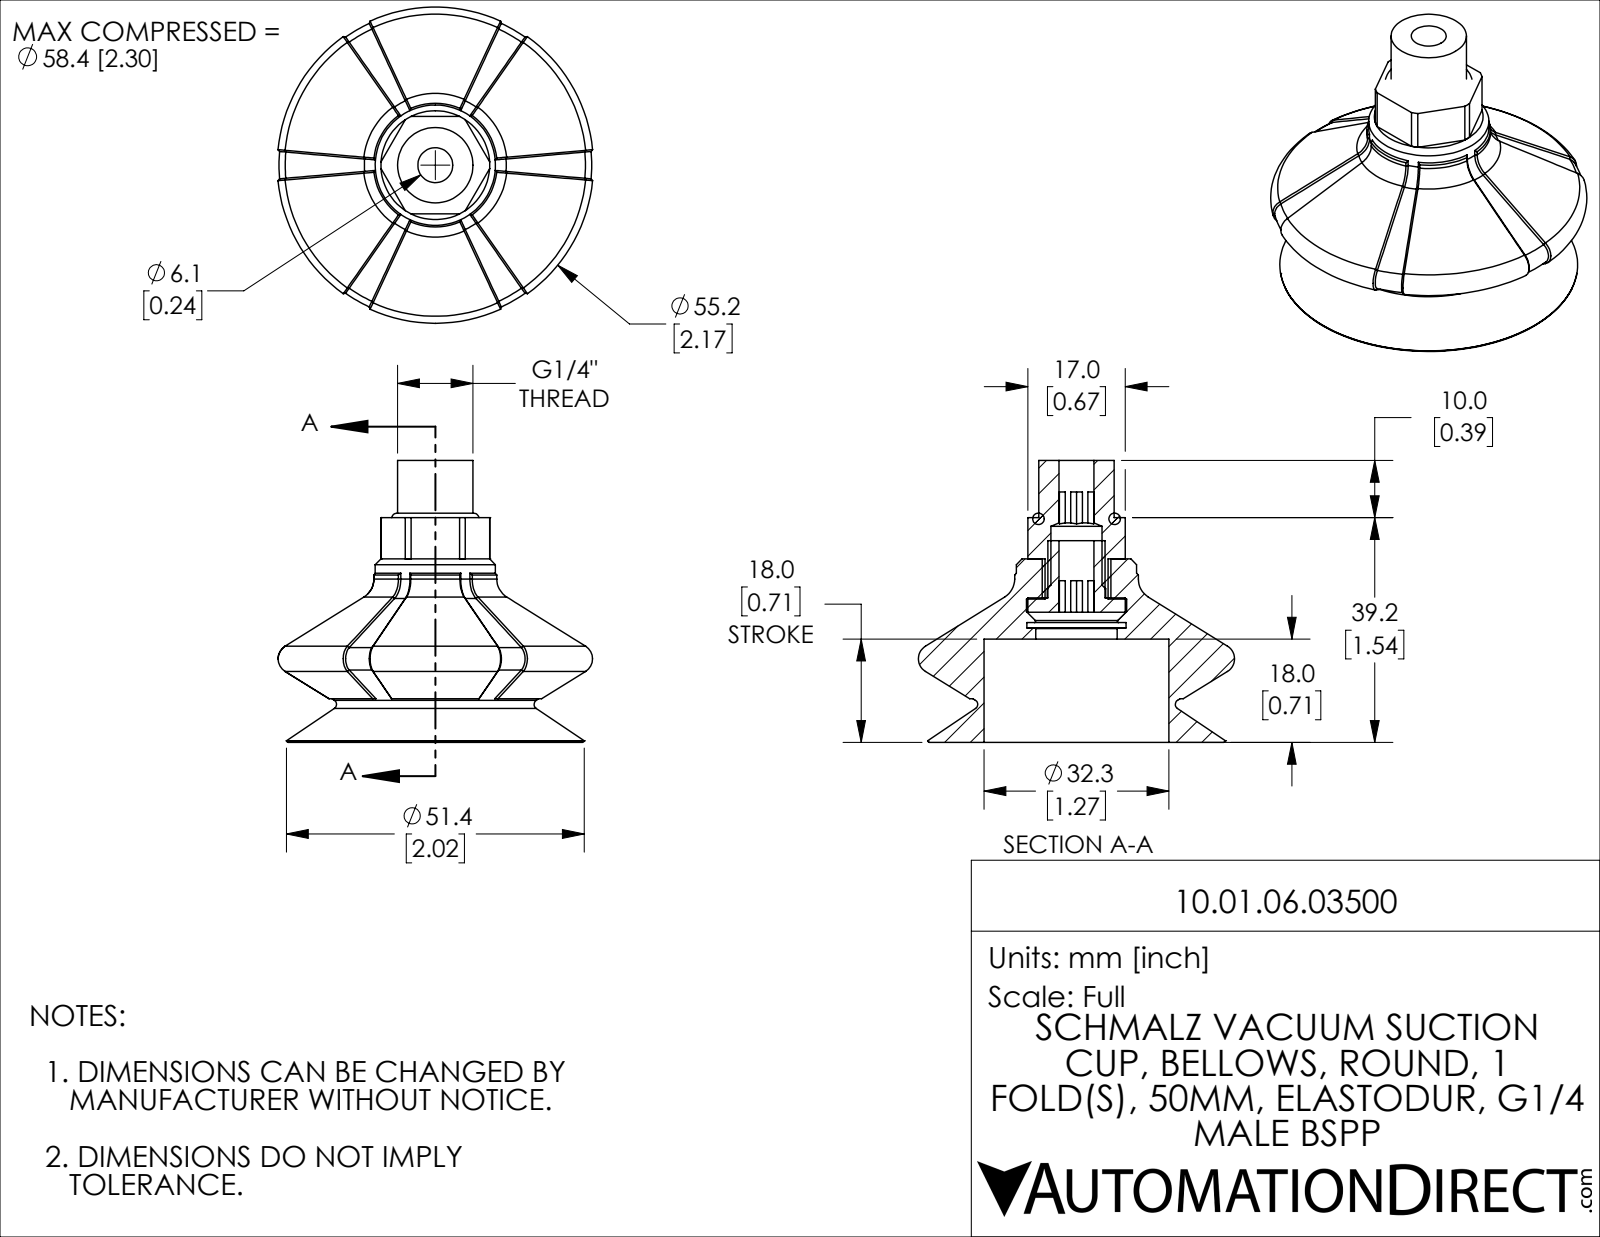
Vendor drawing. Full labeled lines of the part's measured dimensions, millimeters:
Part name (STEP PRODUCT): 10.01.06.03500
STEP written by: SolidWorks 2021 (CONFIG_CONTROL_DESIGN)
Units: millimetres
Bodies: 4 solids, 253 faces (72 planar, 41 cylindrical, 140 other)
Overall size (bounding box): 55.2 × 54.94 × 49.2
Volume: 28 551 mm³ · Surface area: 14 794 mm²
Round holes (diameter × count): ⌀6.1 ×1, ⌀8.92 ×1, ⌀10.2 ×1, ⌀11 ×1, ⌀14.22 ×1, ⌀17.3 ×1, ⌀17.5 ×1, ⌀32.3 ×1
Round bosses / shafts (diameter × count): ⌀21 ×1, ⌀17 ×1, ⌀13.16 ×1, ⌀12 ×1, ⌀10 ×1
Partial cylindrical surfaces — rounded edges, fillets, slot ends (radius × count): R9.5 ×1, R10.8 ×1
Main face-to-face distances: 18, 14, 32, 7, 7.2, 22.7, 4.7, 9.3, 17, 25.2
